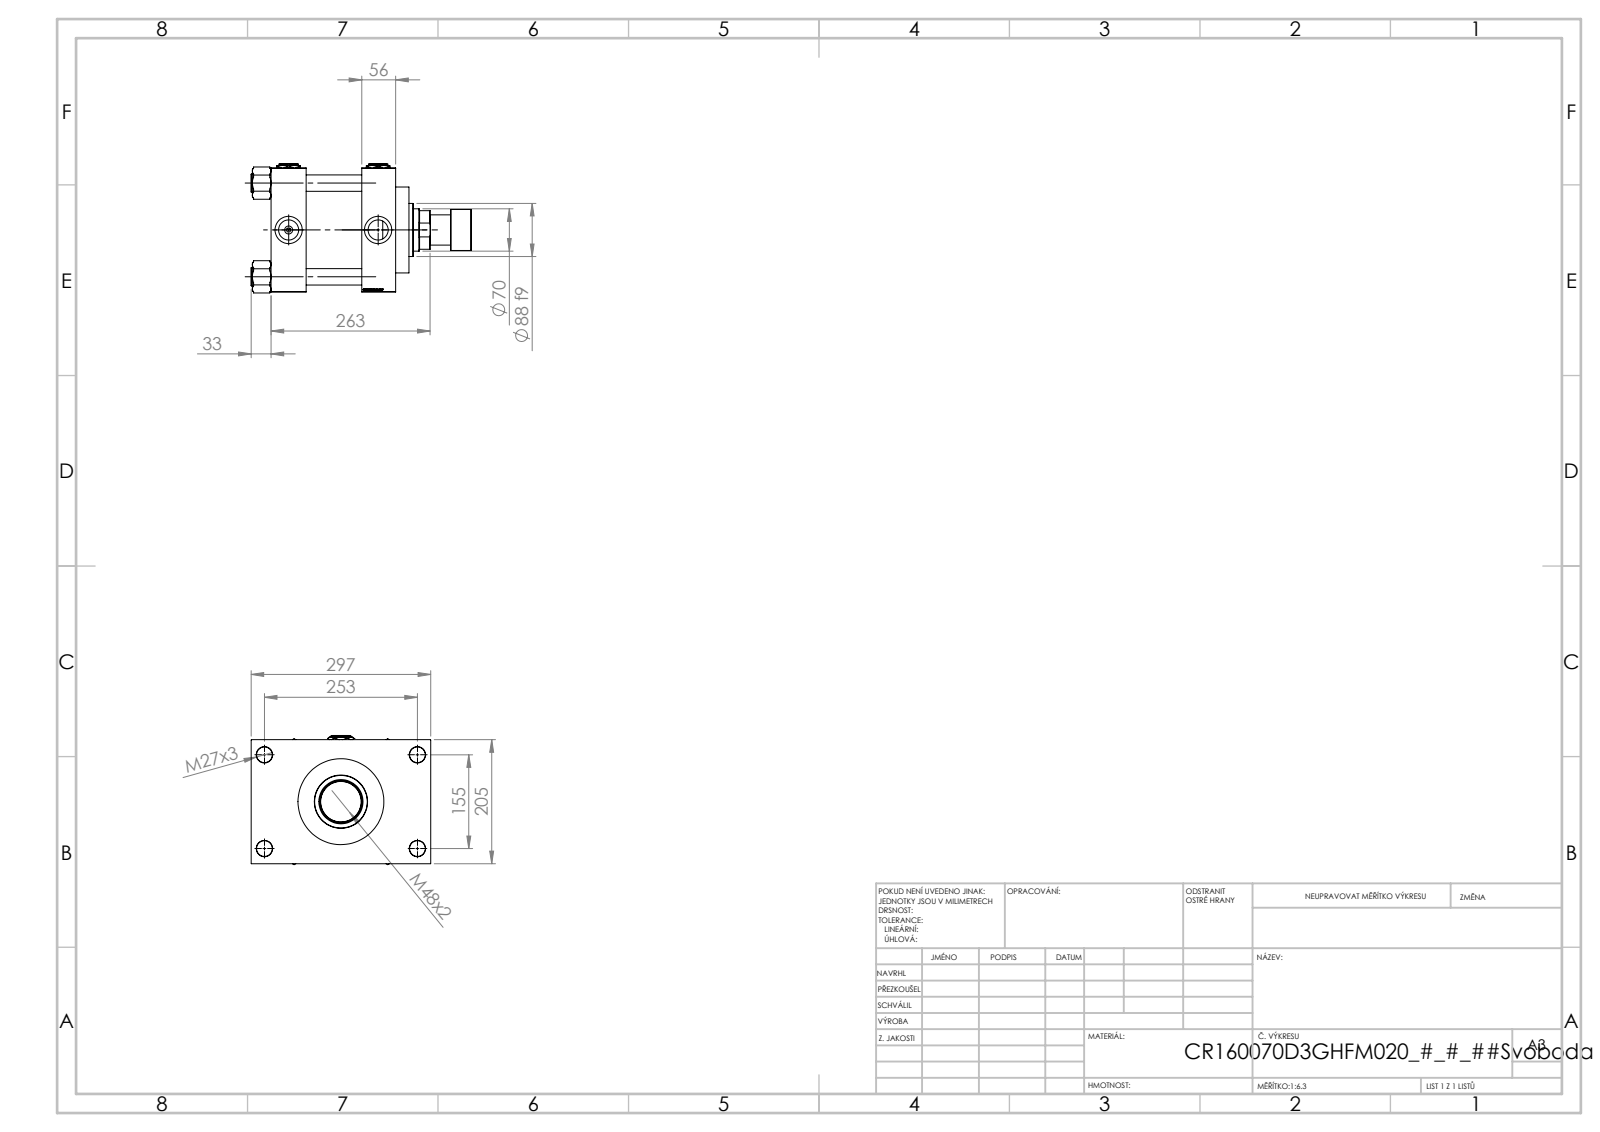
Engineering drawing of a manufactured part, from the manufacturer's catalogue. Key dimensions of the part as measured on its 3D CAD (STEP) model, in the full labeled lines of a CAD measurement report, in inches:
Part name (STEP PRODUCT): V215CR_ROD_END_F; NUT_M5_D; V215_VC_A; V215CR_VCP_D (+3 more)
STEP written by: SolidWorks 2019 (CONFIG_CONTROL_DESIGN)
Units: inches
Bodies: 14 solids, 1263 faces (596 planar, 103 cylindrical, 564 other)
Overall size (bounding box): 14.331 × 11.693 × 8.408
Volume: 489 in³ · Surface area: 1 180 in²
Round holes (diameter × count): ⌀1.024 ×4, ⌀1.063 ×4, ⌀1.309 ×4, ⌀1.772 ×4, ⌀0.276 ×3, ⌀1.831 ×1, ⌀2.756 ×1, ⌀2.874 ×1, ⌀4.724 ×1, ⌀5.591 ×1, ⌀6.299 ×1
Round bosses / shafts (diameter × count): ⌀1.181 ×4, ⌀6.535 ×1, ⌀3.465 ×1, ⌀2.677 ×1, ⌀1.969 ×1, ⌀1.929 ×1
Main face-to-face distances: 2.283, 5.906, 3.622, 5.827, 8.11, 2.205, 8.071, 1.811, 9.882, 2.835
Hole centre spacings: 1.931, 4.312, 5.841, 6.098, 6.399, 8.03, 10.084, 5.827
